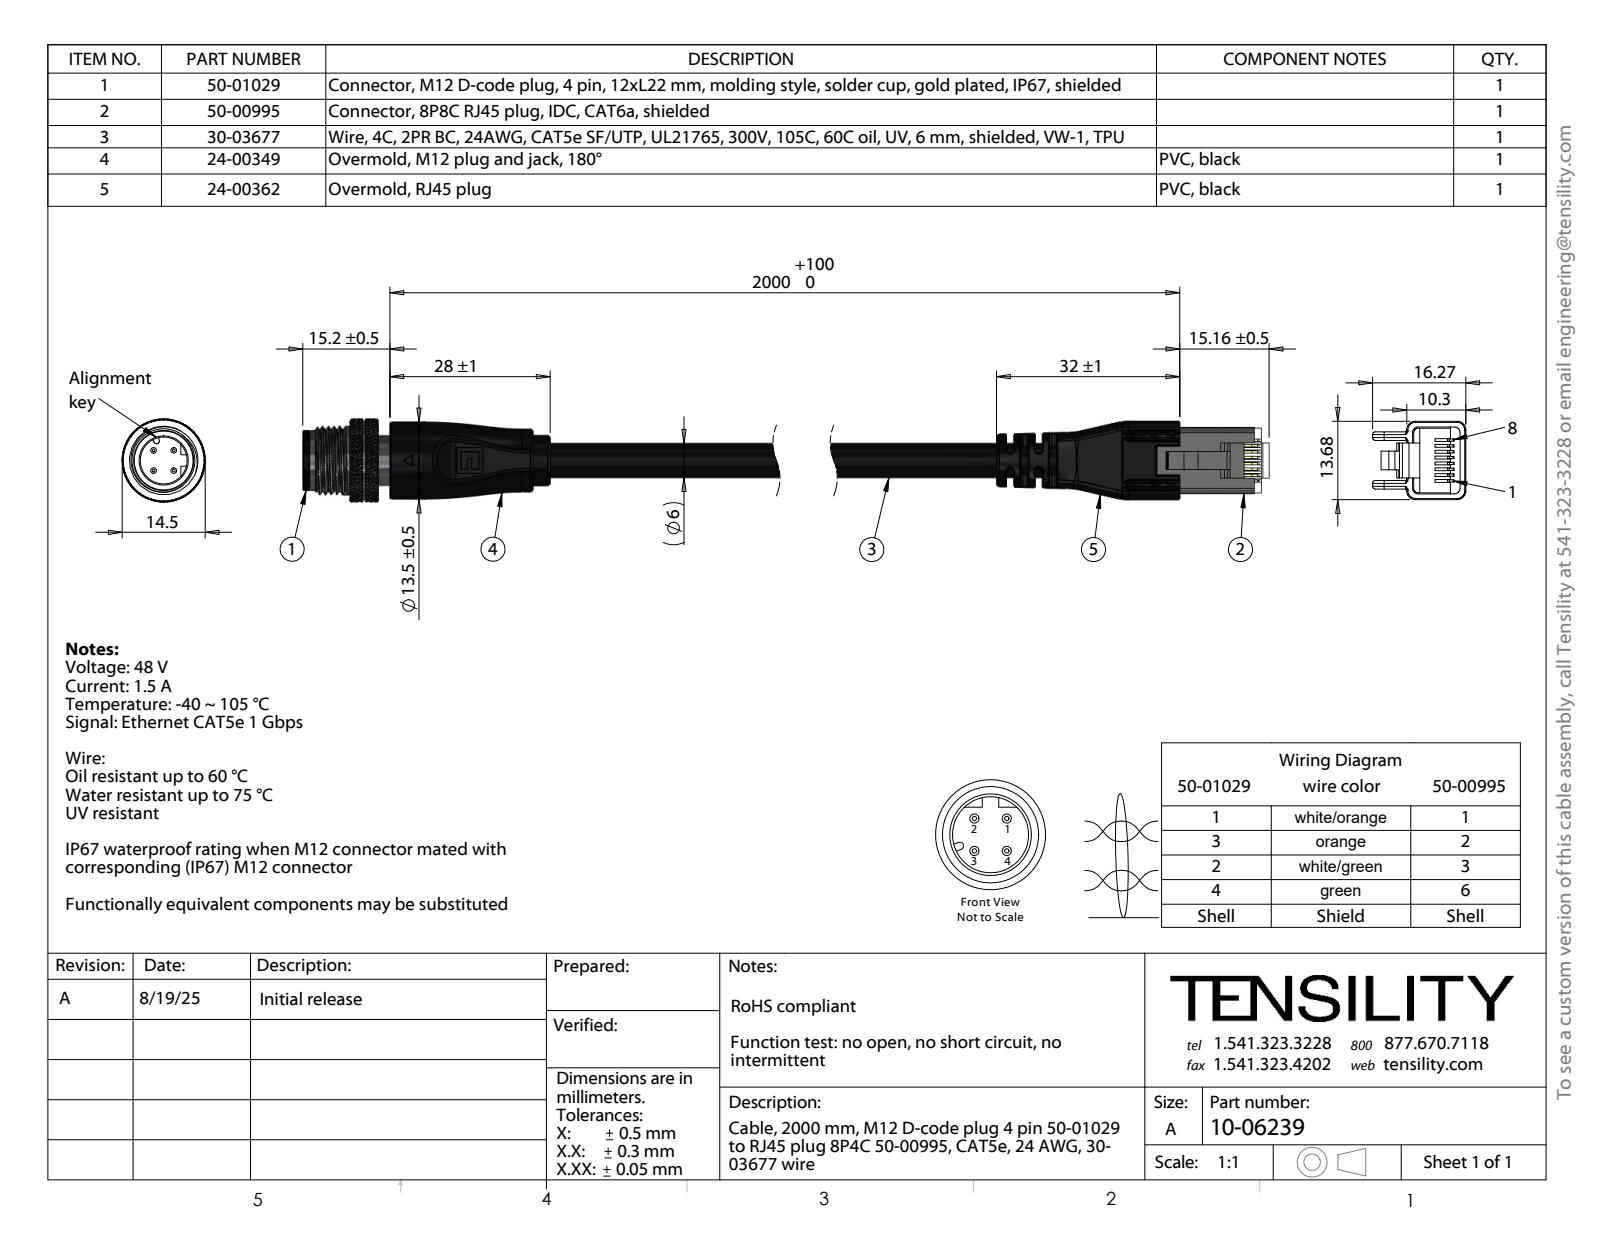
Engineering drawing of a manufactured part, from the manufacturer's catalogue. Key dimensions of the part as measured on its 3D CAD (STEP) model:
Part name (STEP PRODUCT): 50-01029-03_默认; 24-00349_Mexico; 50-01029-01_默认; 50-01029_默认 (+6 more)
STEP written by: SolidWorks 2025 (CONFIG_CONTROL_DESIGN)
Units: millimetres
Bodies: 54 solids, 3209 faces (470 planar, 811 cylindrical, 1928 other)
Overall size (bounding box): 230.31 × 18.37 × 14.5
Volume: 13 919 mm³ · Surface area: 29 131 mm²
Round holes (diameter × count): ⌀0.2 ×28, ⌀1 ×4, ⌀1.05 ×4, ⌀3.16 ×1, ⌀3.21 ×1, ⌀3.56 ×1, ⌀8 ×1, ⌀8.2 ×1, ⌀8.8 ×1, ⌀9.5 ×1
Round bosses / shafts (diameter × count): ⌀1.4 ×4, ⌀14.5 ×1, ⌀13.9 ×1, ⌀13.5 ×1, ⌀12 ×1, ⌀11 ×1, ⌀10.5 ×1, ⌀9.3 ×1
Partial cylindrical surfaces — rounded edges, fillets, slot ends (radius × count): R0.2 ×11, R0.5 ×10, R1.5 ×10, R0.62 ×8, R1 ×5, R10 ×4, R0.8 ×2, R1.15 ×2
Main face-to-face distances: 1.25, 2.5, 1, 3.75, 5, 9.3, 7, 199.5, 12.68, 11.68
Hole centre spacings: 1.06, 1.91, 2.09, 0.35, 1.08, 1.71, 1.8, 2.26
